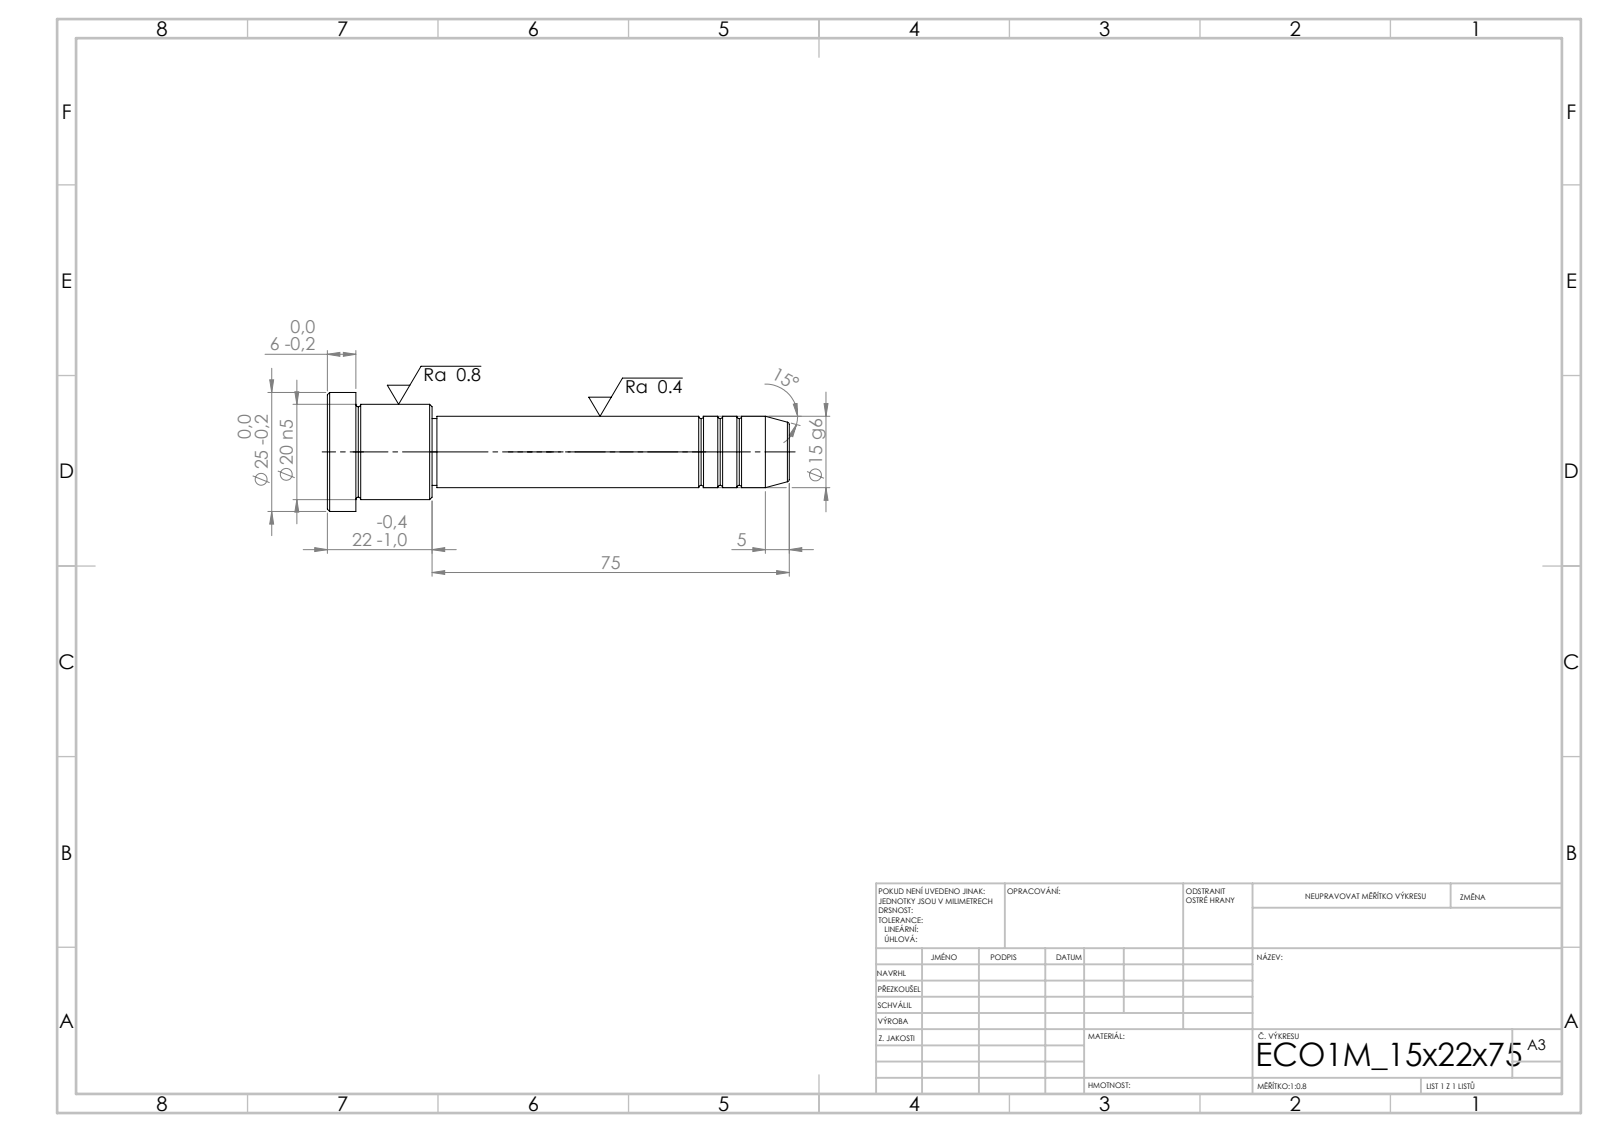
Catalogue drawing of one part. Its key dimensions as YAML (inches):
step_written_by: "SolidWorks 2019 (CONFIG_CONTROL_DESIGN)"
units: inches
bodies: {solids: 1, faces: 43, planar: 5, cylindrical: 14, other: 24}
overall_size: [3.819, 0.984, 0.984]
volume: 1.279
surface_area: 9.334
round_bosses_or_shafts:
  - {diameter: 0.984, count: 1}
  - {diameter: 0.787, count: 1}
  - {diameter: 0.591, count: 1}
  - {diameter: 0.551, count: 1}
face_to_face_distances: [0.236, 0.63, 0.866, 2.953, 3.583, 3.819, 2.913, 0.039, 0.669, 0.906]
